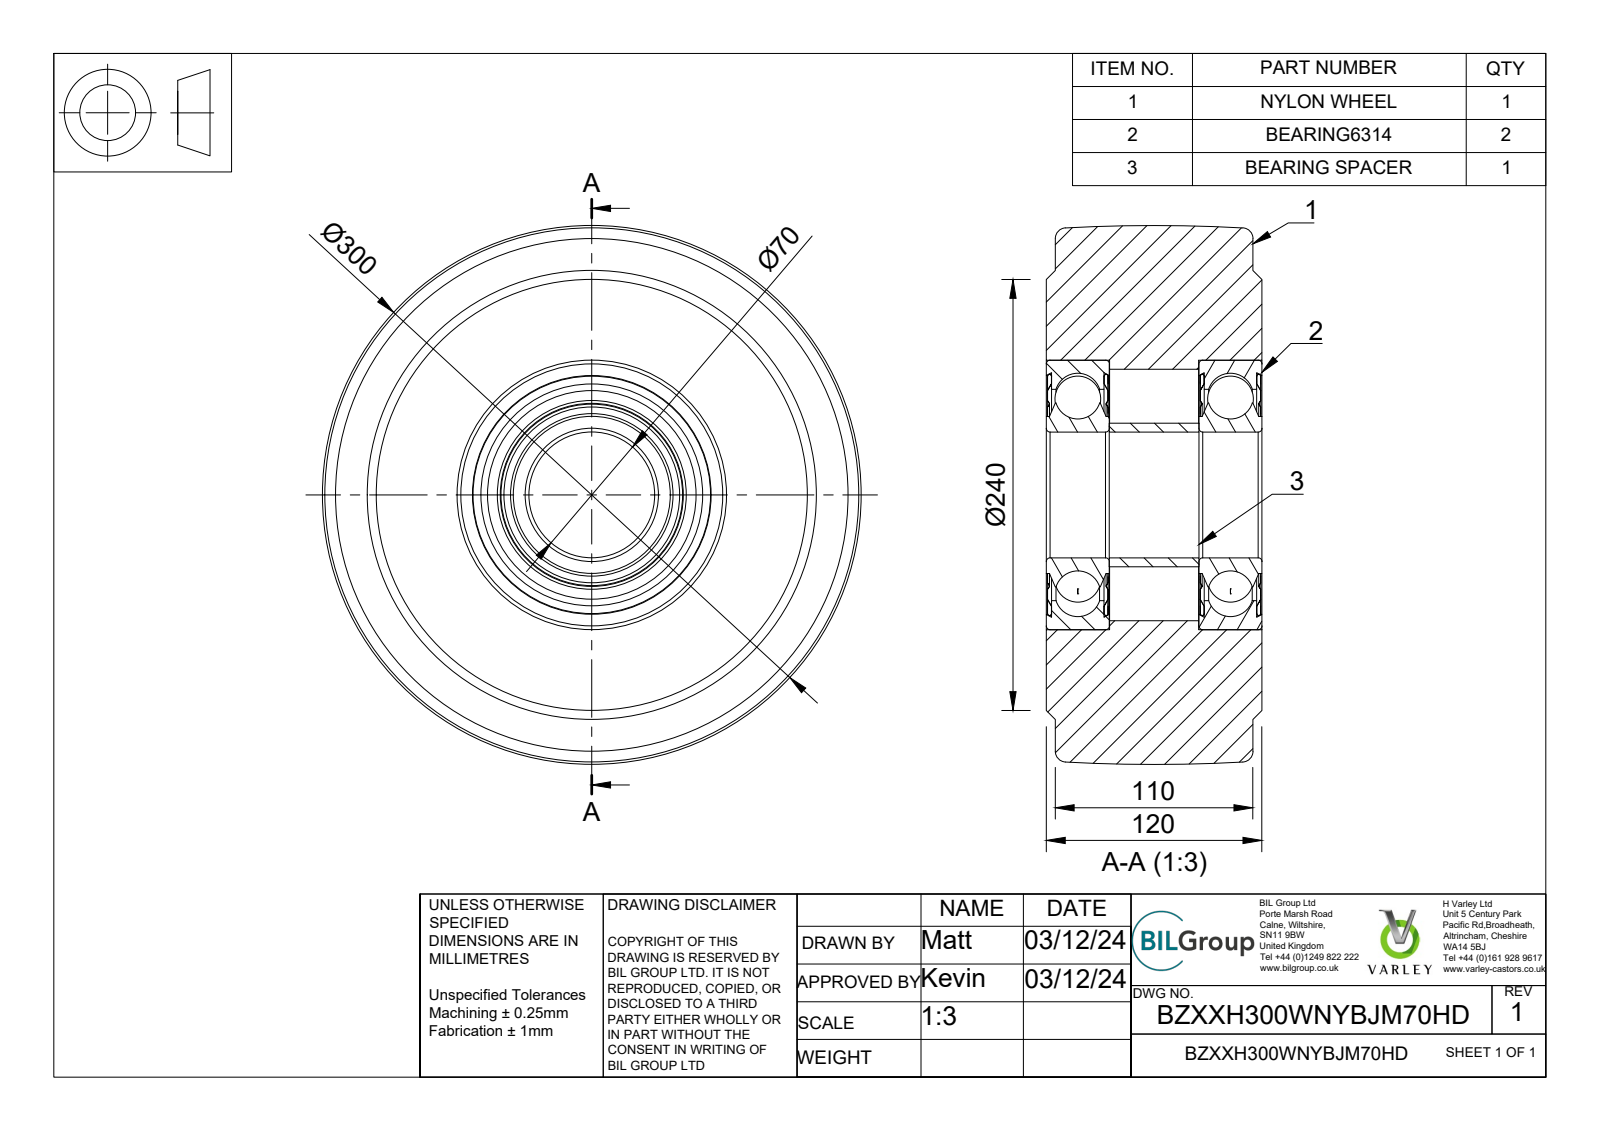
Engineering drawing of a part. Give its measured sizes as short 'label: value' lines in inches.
name: BZXXH300WNYBJM70HD v2; NYLON WHEEL; BEARING SPACER; BEARING6314 (+1 more)
written by: Autodesk Translation Framework v13.20.0.188 (AP242_MANAGED_MODEL_BASED_3D_ENGINEERING_MIM_LF)
unit: in
bodies: 12 solids, 178 faces (60 planar, 29 cylindrical, 89 other)
size: 11.811 × 11.811 × 4.724
volume: 418.7 in³; area: 870.2 in²
holes: 1× ⌀2.756, 1× ⌀3.561, 1× ⌀4.631, 1× ⌀4.862, 1× ⌀5.512, 1× ⌀5.906
bosses: 1× ⌀4.031, 1× ⌀3.441, 1× ⌀3.15
face distances: 3.346, 4.724, 0.197, 4.528, 0.115, 1.263, 0.023, 1.355, 0.092, 1.24
